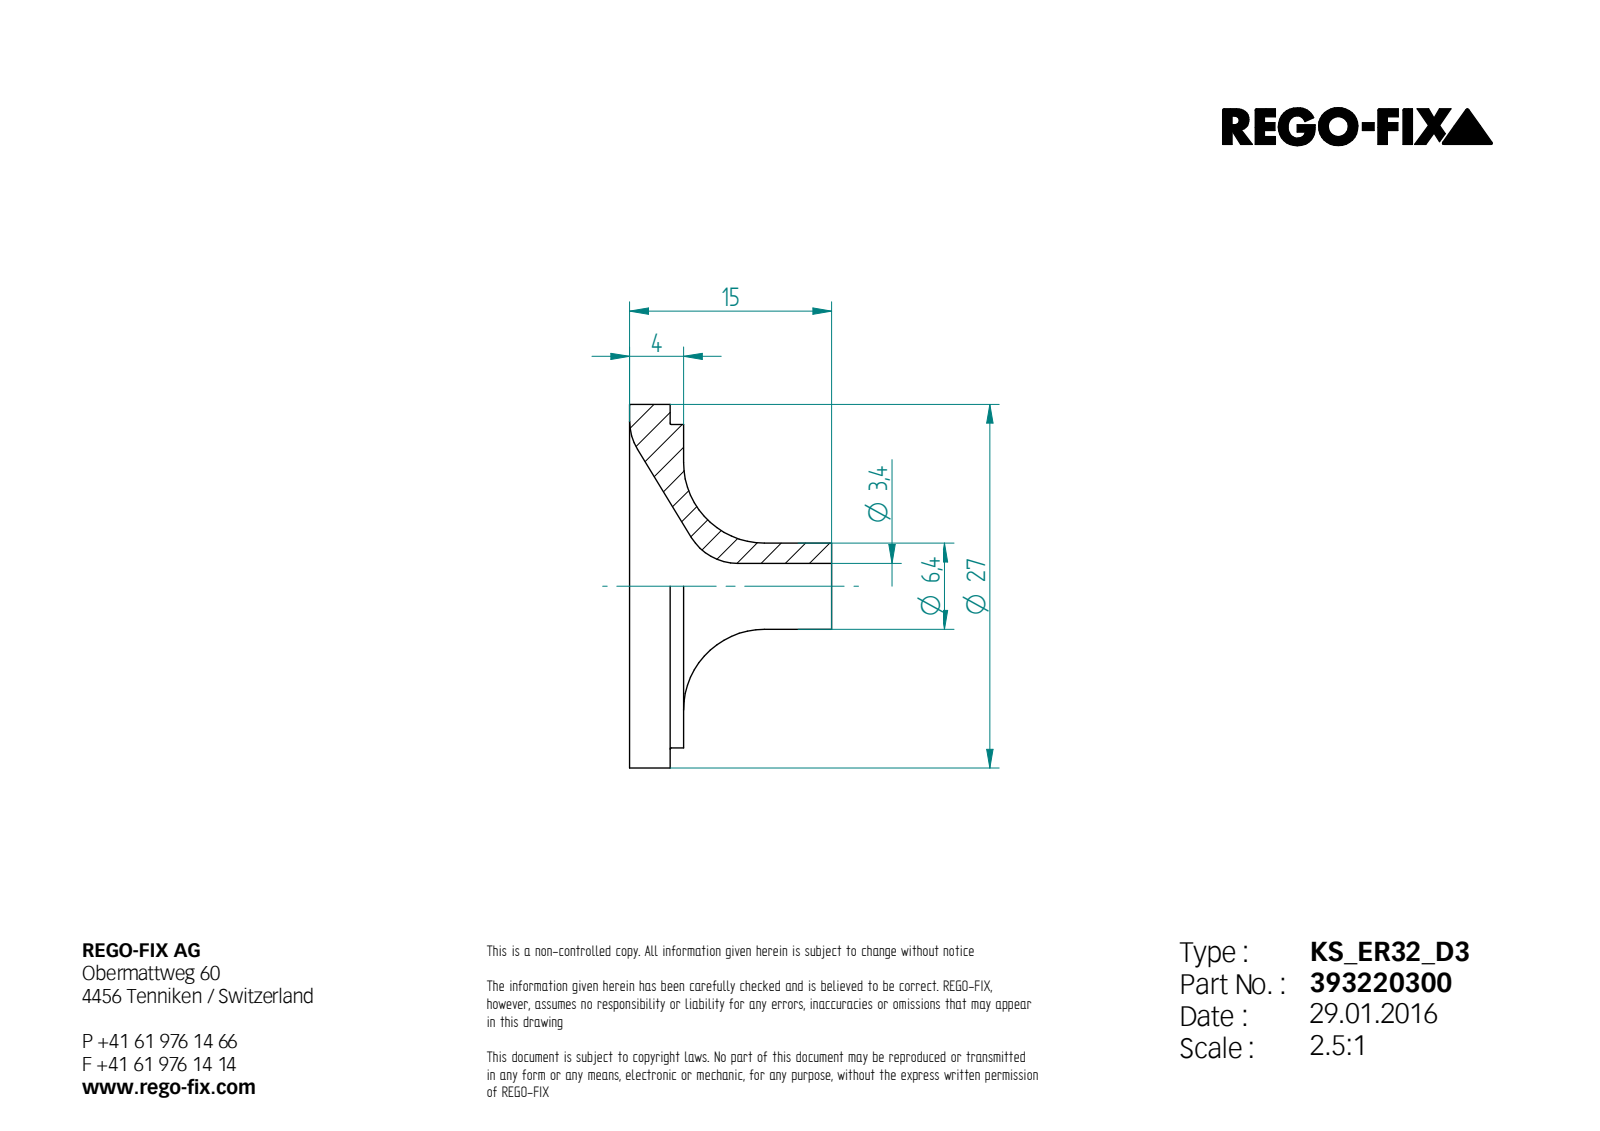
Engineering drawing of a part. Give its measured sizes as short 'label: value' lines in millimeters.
written by: Unknown (AUTOMOTIVE_DESIGN)
unit: mm
bodies: 1 solid, 13 faces (4 planar, 4 cylindrical, 5 other)
size: 27 × 27 × 15
volume: 1 765 mm³; area: 1 798 mm²
holes: 1× ⌀3.4
bosses: 1× ⌀27, 1× ⌀24, 1× ⌀6.4
face distances: 1, 3, 4, 15, 12, 11
